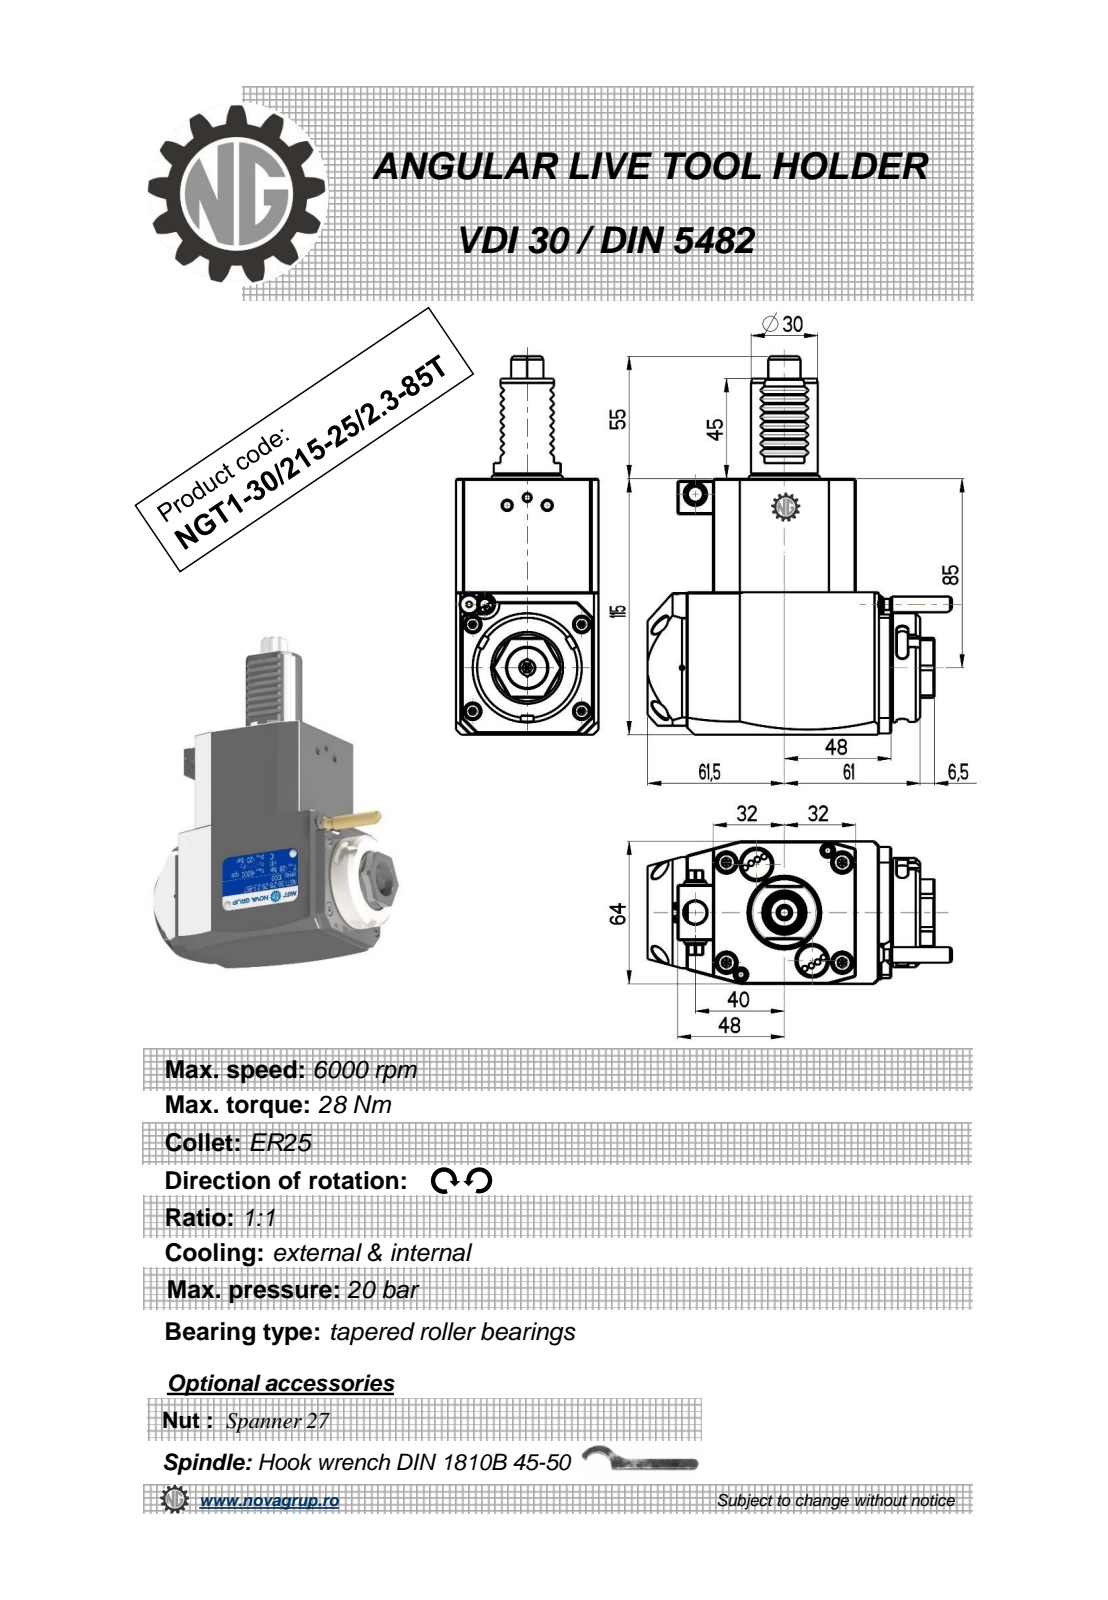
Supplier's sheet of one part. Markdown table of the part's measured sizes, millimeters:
| quantity | value |
| --- | --- |
| part name | NGT1_30_215_25_1_3_85T |
| STEP written by | PRO/ENGINEER BY PARAMETRIC TECHNOLOGY CORPORATION, 2010280 (CONFIG_CONTROL_DESIGN) |
| units | millimeters |
| bodies | 1 solid, 413 faces (203 planar, 120 cylindrical, 90 other) |
| overall size | 170 × 136.88 × 64 |
| volume | 666 455 mm³ |
| surface area | 56 679 mm² |
| round holes (diameter × count) | 2.5 × 1, 3 × 1, 4.2 × 1, 5.3 × 1, 8.5 × 1, 9.5 × 1, 10 × 1, 18 × 1 |
| round bosses / shafts (diameter × count) | 8 × 2, 49 × 1, 42 × 1, 30 × 1, 10 × 1, 7 × 1, 5 × 1 |
| partial cylindrical surfaces (radius × count) | 0.3 × 16, 2.91 × 16, 2.5 × 6, 180 × 2, 3.85 × 1, 4.5 × 1, 5.7 × 1, 7.25 × 1 |
| main face-to-face distances | 64, 115, 16, 80, 13, 51, 29.5, 93.5, 109.5, 72.18 |
| hole center spacings | 34.25, 40, 51.62, 76.5 |
